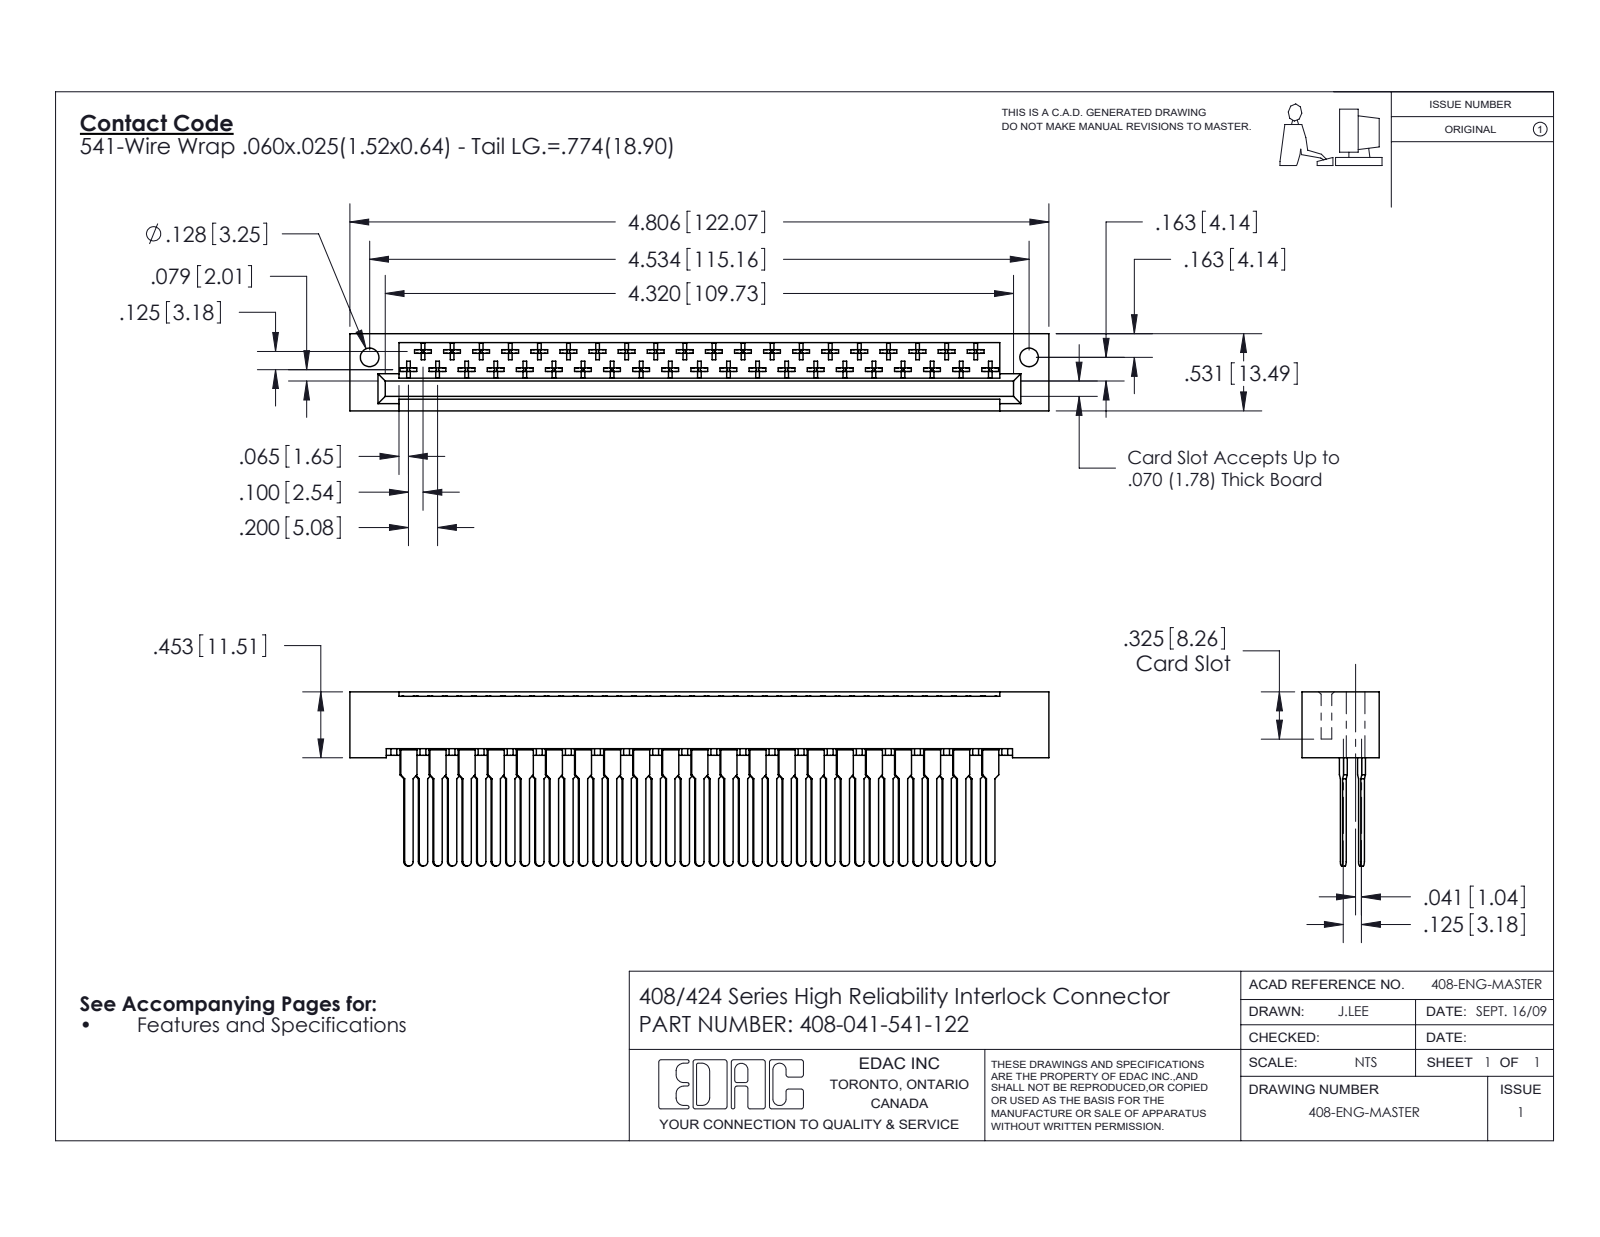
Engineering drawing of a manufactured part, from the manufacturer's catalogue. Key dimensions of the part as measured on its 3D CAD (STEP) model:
Part name (STEP PRODUCT): 408-041-541-122; 408-290-001_408-290-141; 408 Part_041 - 1
STEP written by: SolidWorks 2016 (CONFIG_CONTROL_DESIGN)
Units: inches
Bodies: 42 solids, 2217 faces (1676 planar, 377 cylindrical, 164 other)
Overall size (bounding box): 4.806 × 1.197 × 0.531
Volume: 0.857 in³ · Surface area: 30.65 in²
Round holes (diameter × count): ⌀0.128 ×2
Partial cylindrical surfaces — rounded edges, fillets, slot ends (radius × count): R0.01 ×246, R0.02 ×43, R0.03 ×41
Main face-to-face distances: 0.1, 0.296, 0.531, 0.125, 0.025, 0.025, 0.259, 0.272, 0.235, 0.135
Hole centre spacings: 4.534
